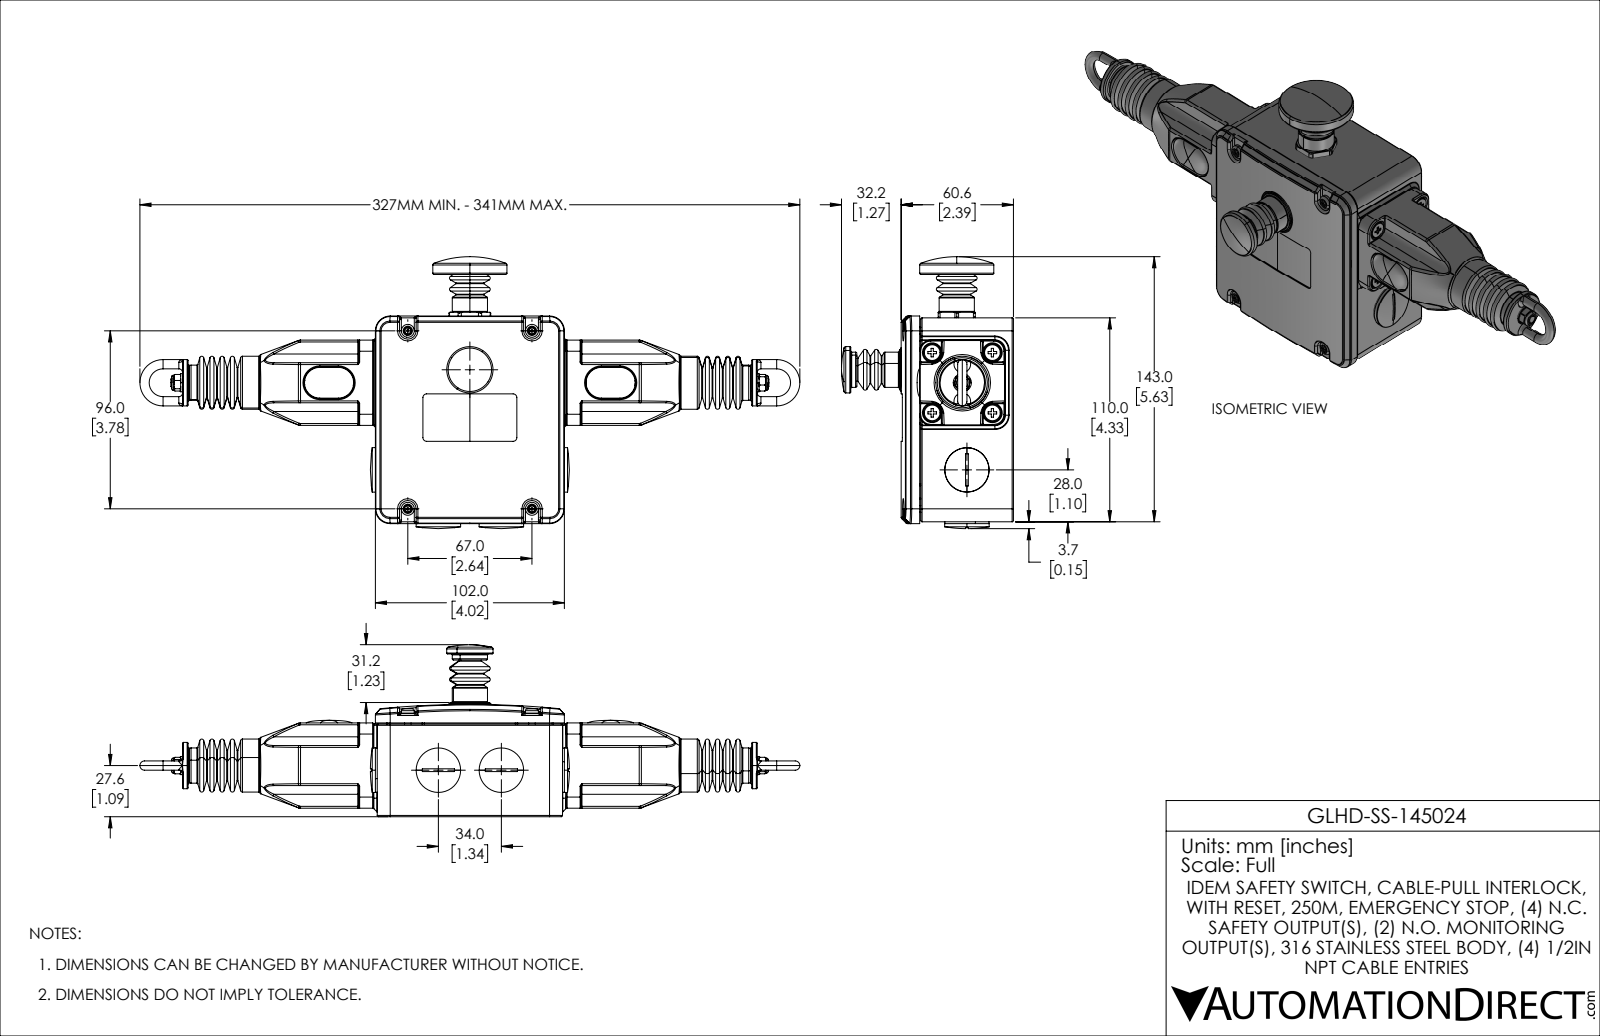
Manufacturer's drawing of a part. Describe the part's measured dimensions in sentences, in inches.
The part is named "GLHD-SS-145024". Its 3-D file was written by "SolidWorks 2021 (AUTOMOTIVE_DESIGN)". It is 43 solids with 4313 faces: 977 planar, 1468 cylindrical and 1868 other. Overall it measures 14.024 by 5.775 by 3.654 inches. Its volume is 21.45 cubic inches and its surface area 333.3 square inches. Round holes: 9 of diameter 0.197, 6 of diameter 0.354, 5 of diameter 0.209, 4 of diameter 0.094, 4 of diameter 0.13, 4 of diameter 0.157, 4 of diameter 0.161, 4 of diameter 0.189, 4 of diameter 0.213, 4 of diameter 0.228, 4 of diameter 0.378, 3 of diameter 0.118. Round bosses or shafts: 7 of diameter 0.197, 5 of diameter 0.276, 4 of diameter 0.787, 4 of diameter 0.335, 4 of diameter 0.173, 4 of diameter 0.138, 4 of diameter 0.051, 3 of diameter 0.945. Partial cylindrical surfaces (rounded edges, fillets, slot ends): 252 of radius 0.02, 136 of radius 0.039, 64 of radius 0.008, 56 of radius 0.028, 18 of radius 0.012, 18 of radius 0.079, 14 of radius 0.006, 12 of radius 0.004. The main face-to-face distances are 0.039, 2.181, 0.138, 0.079, 2.067, 0.114, 0.157, 4.016, 0.217, 0.335. The hole center spacings are 1.28, 0.905, 0.374, 0.902, 0.907, 1.339, 1.809, 1.891.
